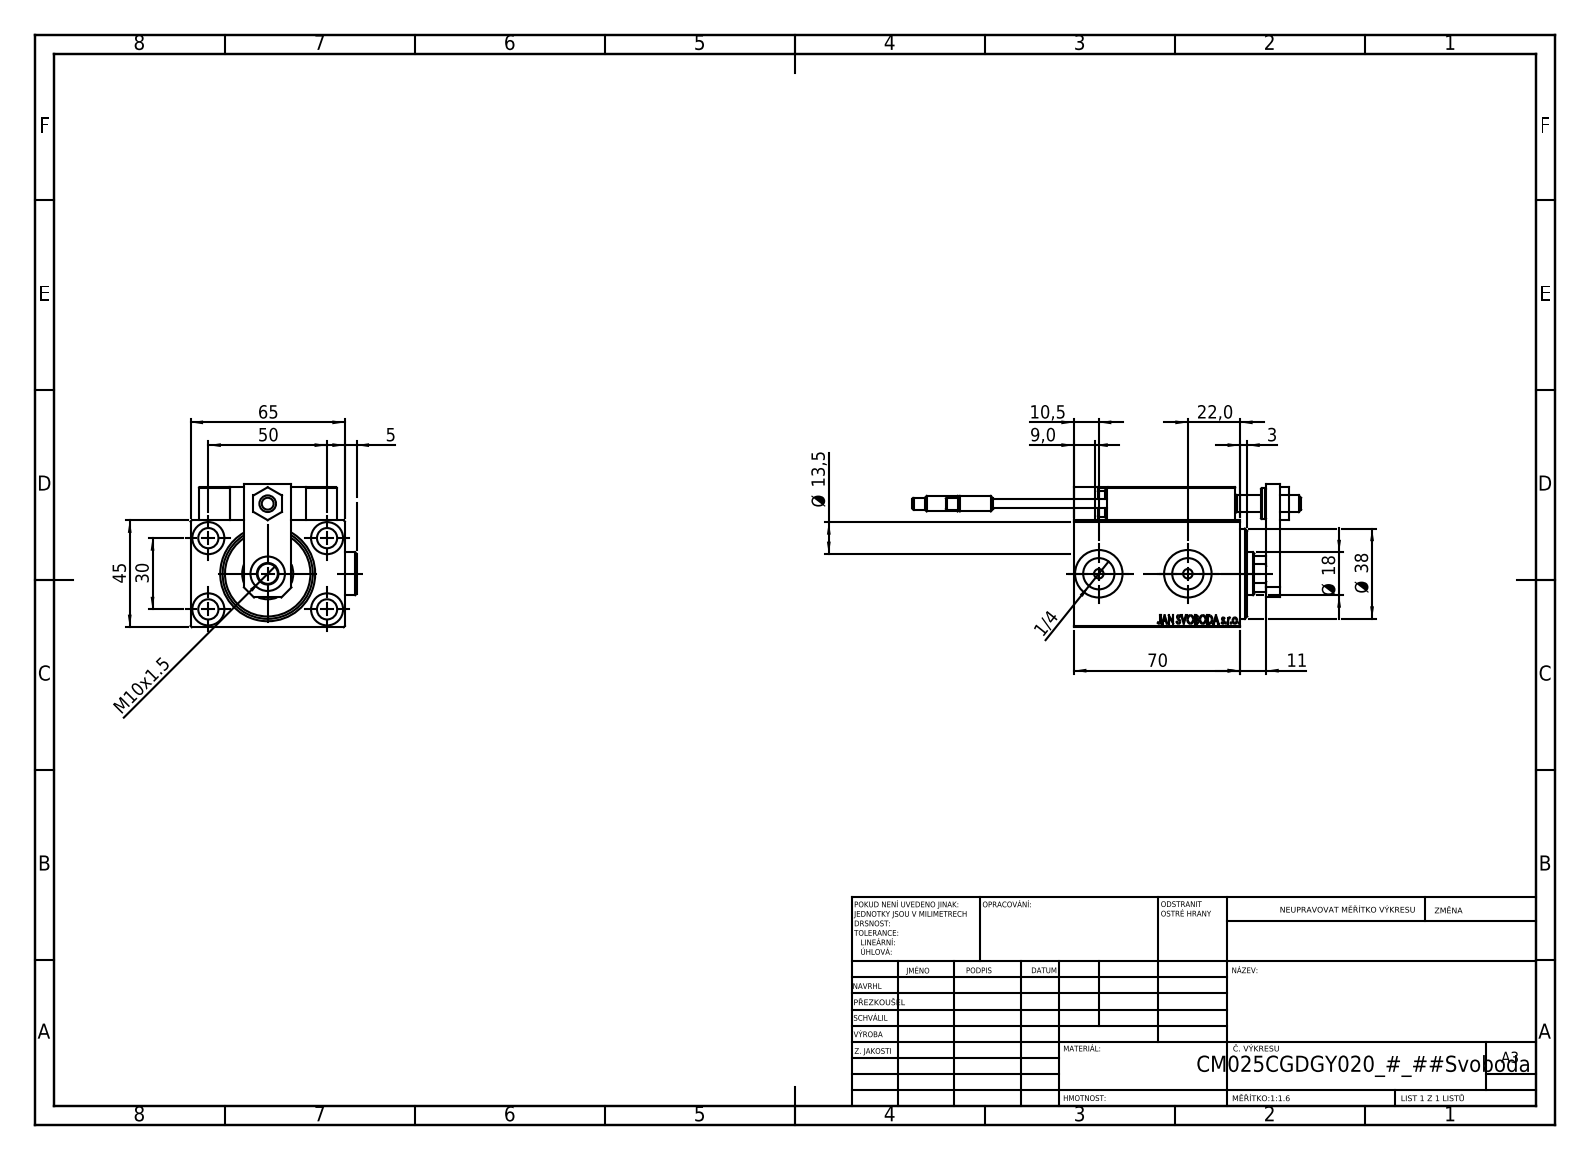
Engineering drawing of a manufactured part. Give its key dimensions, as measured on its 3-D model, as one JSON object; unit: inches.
{"part_name": "V450CM_C_VCP; Zatka_OIL_PORT; V450CM_C_Body; ALLEN BOLT D8 (+7 more)", "step_written_by": "SolidWorks 2019 (CONFIG_CONTROL_DESIGN)", "units": "inches", "bodies": {"solids": 25, "faces": 1358, "planar": 596, "cylindrical": 212, "other": 550}, "overall_size": [6.445, 2.752, 2.382], "volume_in3": 13.6, "surface_area_in2": 113, "round_holes": [[0.157, 6], [0.315, 5], [0.335, 5], [0.126, 4], [0.531, 4], [0.197, 2], [0.518, 2], [0.787, 2], [0.276, 1], [0.571, 1], [0.709, 1], [0.846, 1]], "round_bosses_or_shafts": [[0.197, 4], [0.709, 2], [0.256, 2], [0.15, 2], [0.512, 1], [0.433, 1]], "partial_cylinders_radius": [[0.012, 30], [0.118, 2], [0.335, 1]], "face_to_face_distances": [1.772, 2.323, 0.551, 2.559, 0.236, 0.197, 0.118, 0.748, 0.512, 0.276], "hole_center_spacings": [1.148, 0.448, 0.787, 0.87, 1.138, 1.165, 1.169, 1.181]}
